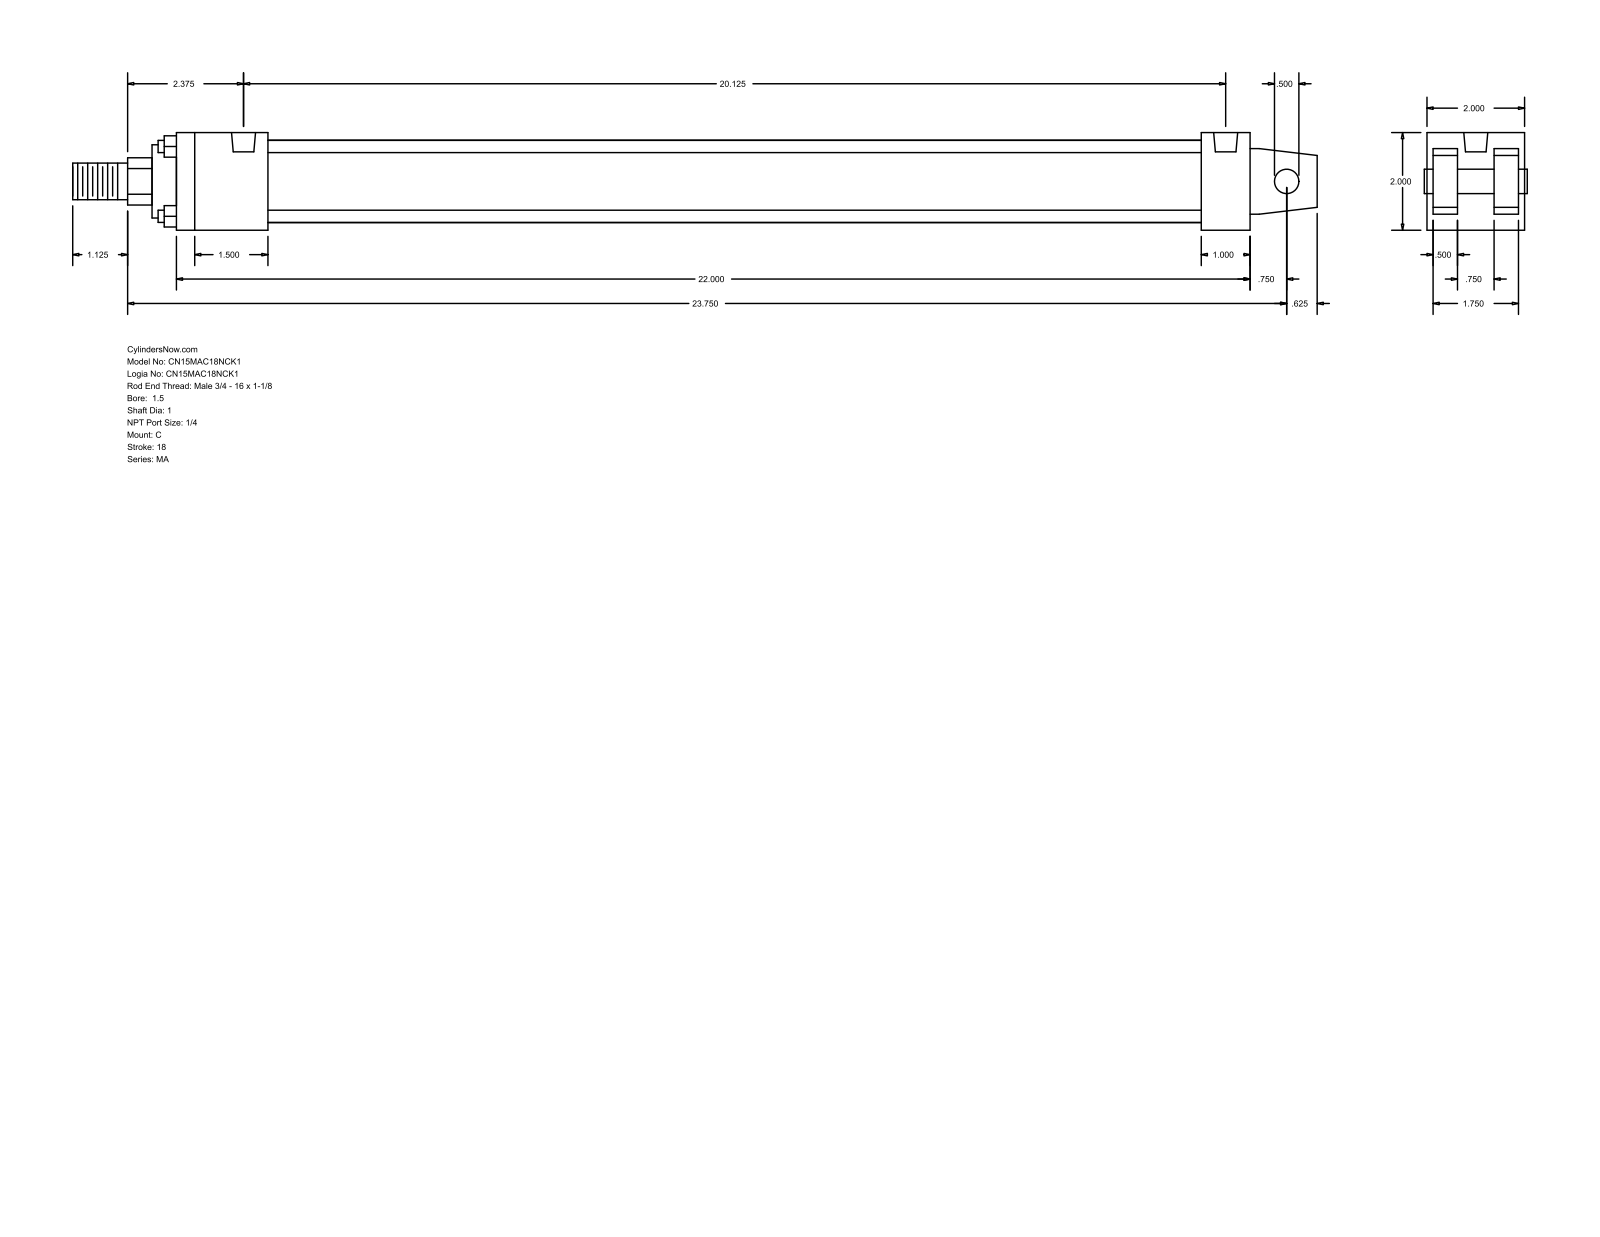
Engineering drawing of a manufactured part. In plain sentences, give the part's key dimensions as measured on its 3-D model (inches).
The part is named "MA_C__0150_1". Its 3-D file was written by "GSSL Pune (CONFIG_CONTROL_DESIGN)". It is 0 solids with 103 faces: 76 planar, 27 cylindrical and 0 other. Overall it measures 25.5 by 2 by 2 inches. Round holes: 4 of diameter 0.313, 2 of diameter 0.492. Round bosses or shafts: 4 of diameter 0.25, 1 of diameter 1.69, 1 of diameter 1.5, 1 of diameter 1, 1 of diameter 0.75, 1 of diameter 0.5. Partial cylindrical surfaces (rounded edges, fillets, slot ends): 1 of radius 0.484. The main face-to-face distances are 2, 1.875, 0.5, 0.125, 0.625, 1.375, 1.25, 22, 1, 21. The hole center spacings are 20.125.
